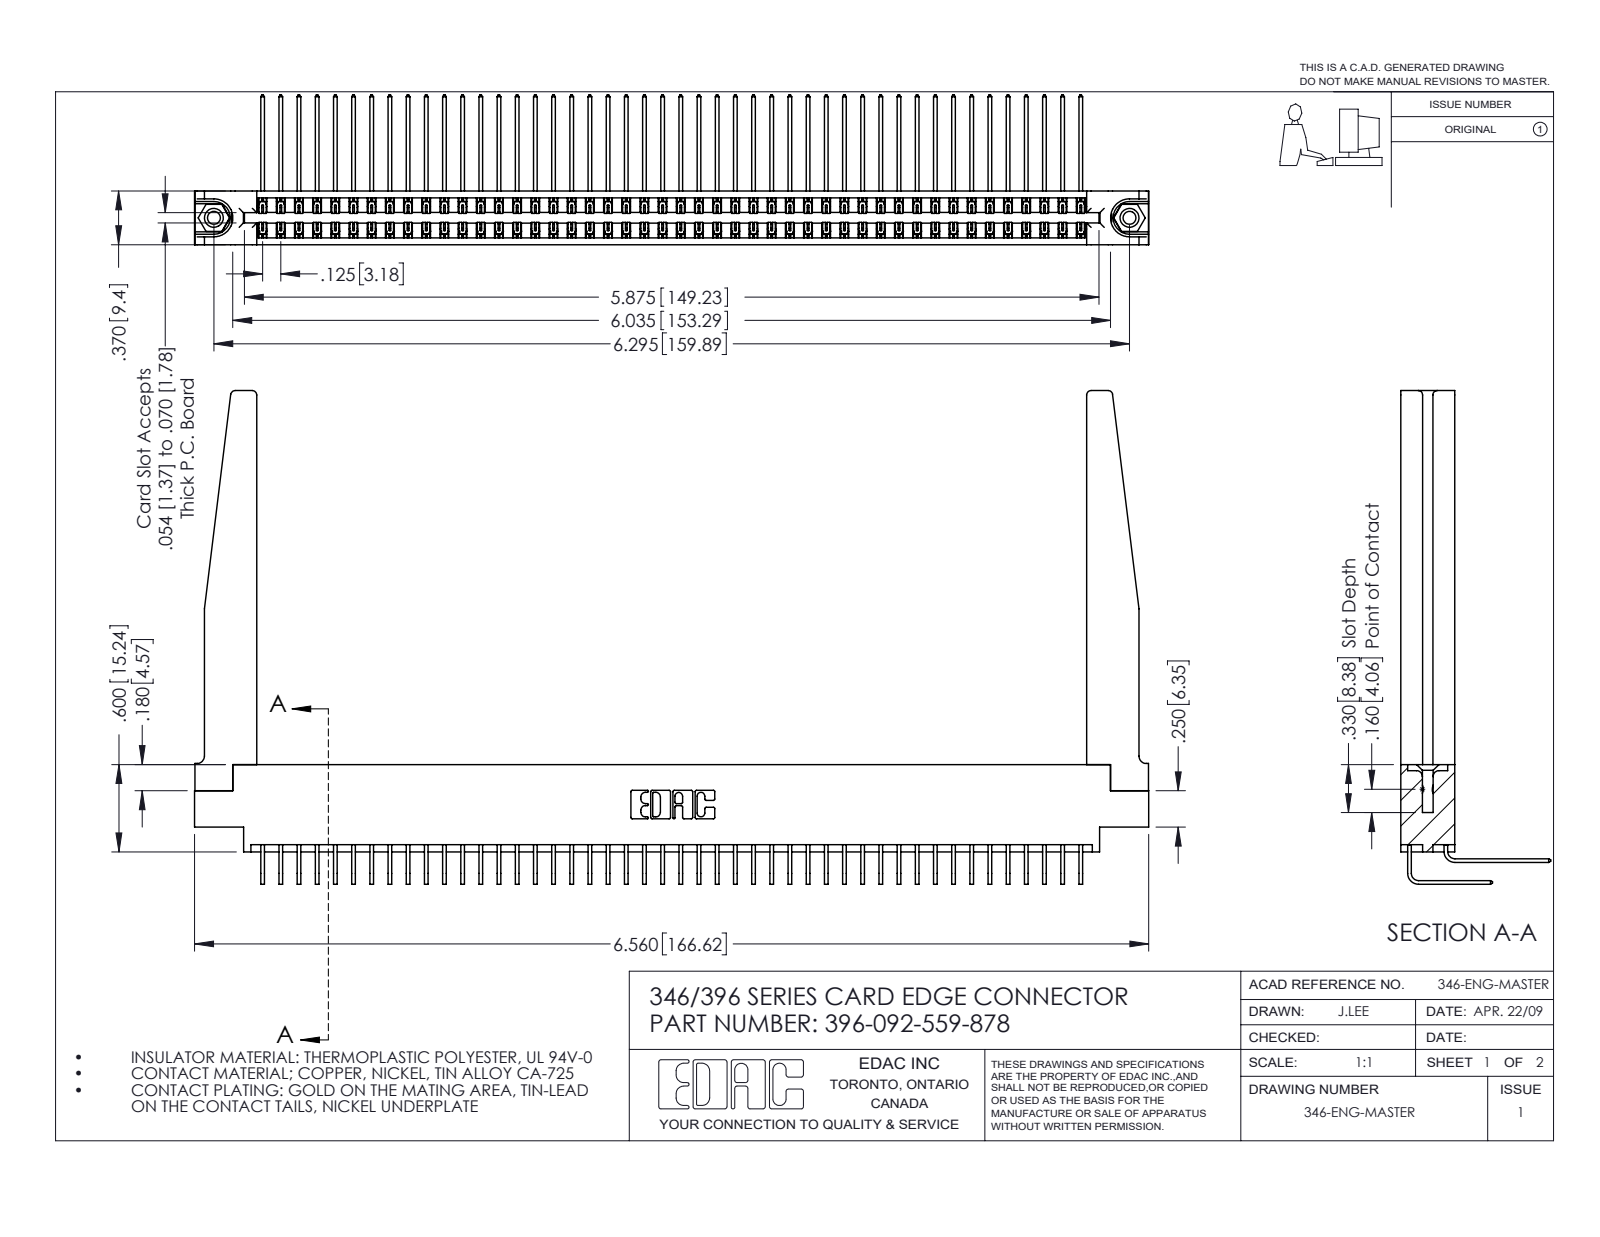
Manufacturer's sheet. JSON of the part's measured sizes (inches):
{"part_name": "346-220-078_345-220-078; 345-250-001_345-250-001-102; 396-092-559-878; 345-292-001_559 Tail - 2 (+2 more)", "step_written_by": "SolidWorks 2016 (CONFIG_CONTROL_DESIGN)", "units": "inches", "bodies": {"solids": 97, "faces": 5328, "planar": 3626, "cylindrical": 1650, "other": 52}, "overall_size": [6.56, 3.393, 1.03], "volume_in3": 1.438, "surface_area_in2": 49.94, "round_holes": [[0.089, 2], [0.125, 2], [0.156, 2], [0.064, 1]], "round_bosses_or_shafts": [[0.155, 2]], "partial_cylinders_radius": [[0.006, 138], [0.01, 22], [0.03, 8], [0.007, 6], [0.031, 6], [0.05, 4], [0.026, 3], [0.014, 2]], "face_to_face_distances": [0.37, 0.048, 0.322, 0.072, 0.025, 0.25, 0.148, 0.15, 0.298, 0.275], "hole_center_spacings": [0.246, 6.086, 6.295]}
